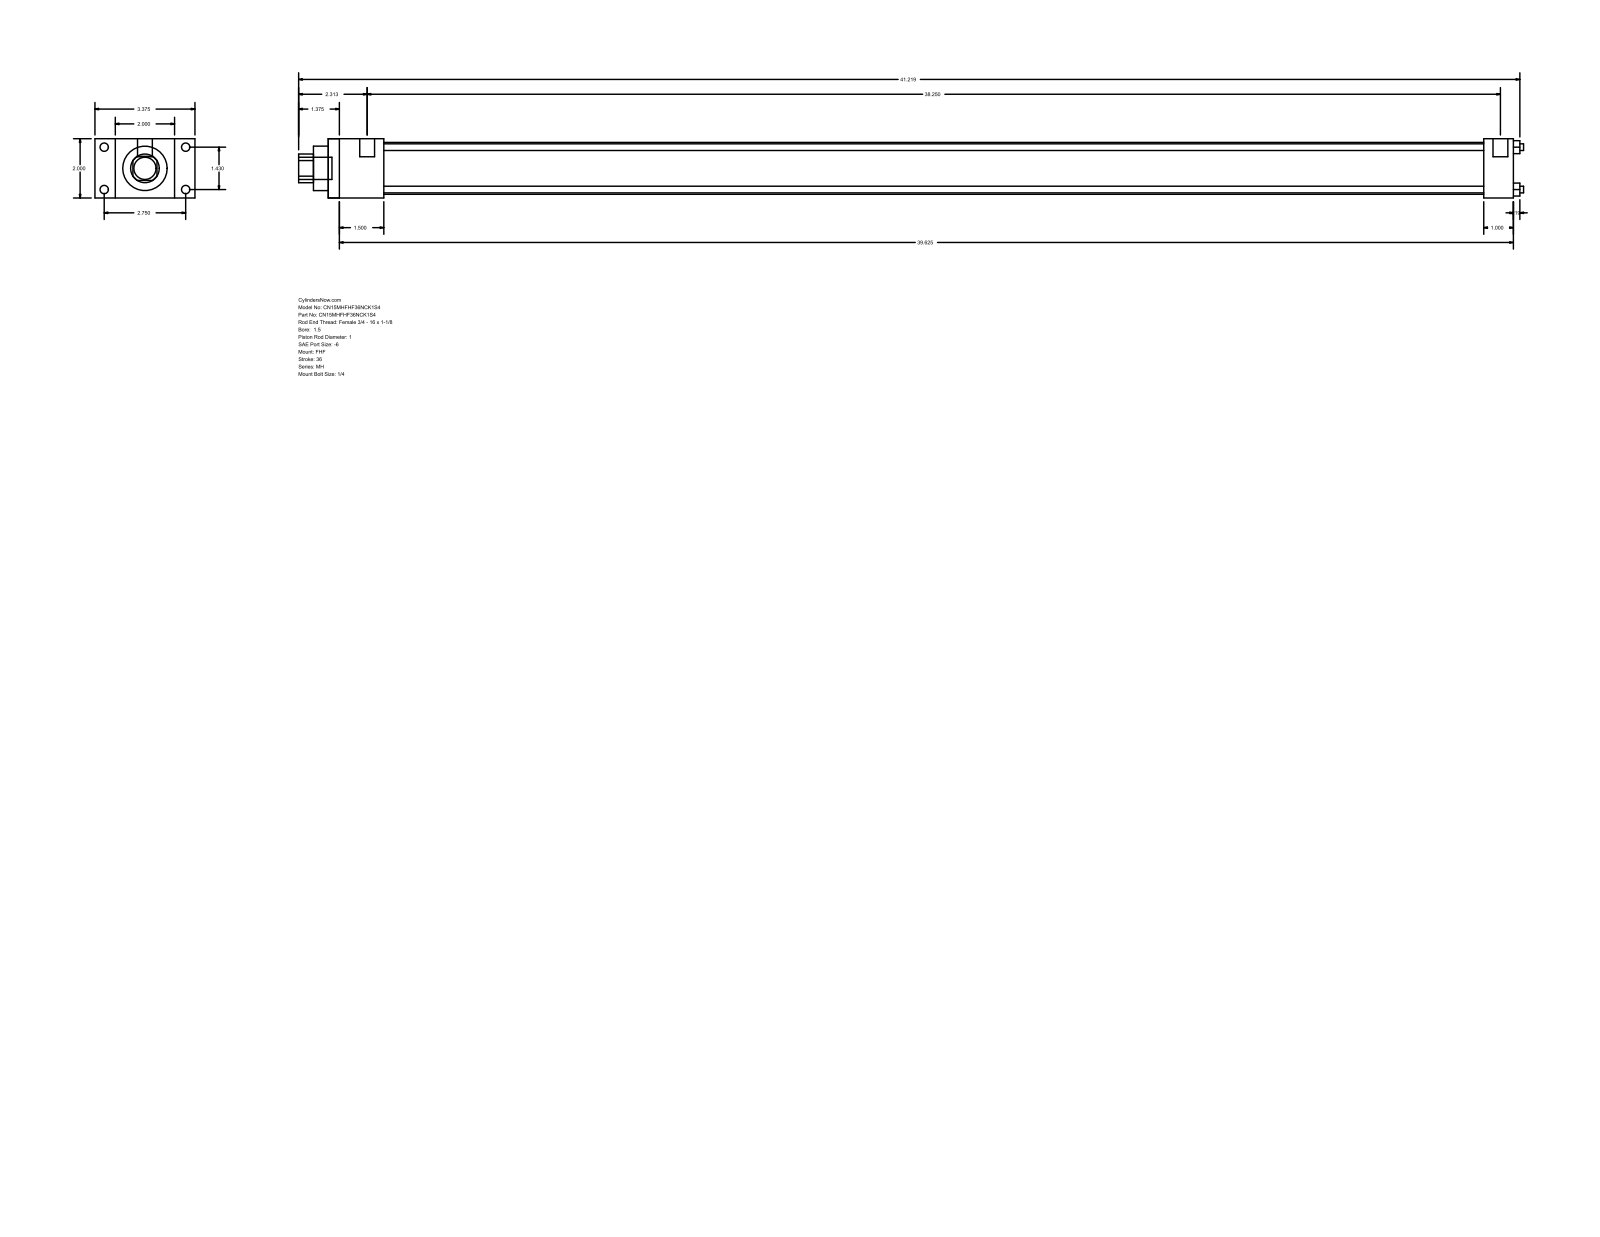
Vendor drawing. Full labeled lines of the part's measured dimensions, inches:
Part name (STEP PRODUCT): MH_FHF__0150_1
STEP written by: GSSL Pune (CONFIG_CONTROL_DESIGN)
Units: inches
Bodies: 0 solids, 88 faces (60 planar, 28 cylindrical, 0 other)
Overall size (bounding box): 41.344 × 3.375 × 2
Round holes (diameter × count): ⌀0.225 ×4, ⌀1 ×1, ⌀1.5 ×1, ⌀1.75 ×1
Round bosses / shafts (diameter × count): ⌀0.281 ×4, ⌀0.219 ×4, ⌀0.5 ×2, ⌀0.75 ×1
Partial cylindrical surfaces — rounded edges, fillets, slot ends (radius × count): R0.484 ×1
Main face-to-face distances: 2, 0.687, 2.687, 1.875, 3.375, 40, 38.125, 1, 39, 37.125
Hole centre spacings: 1.011, 1.43, 2.022
